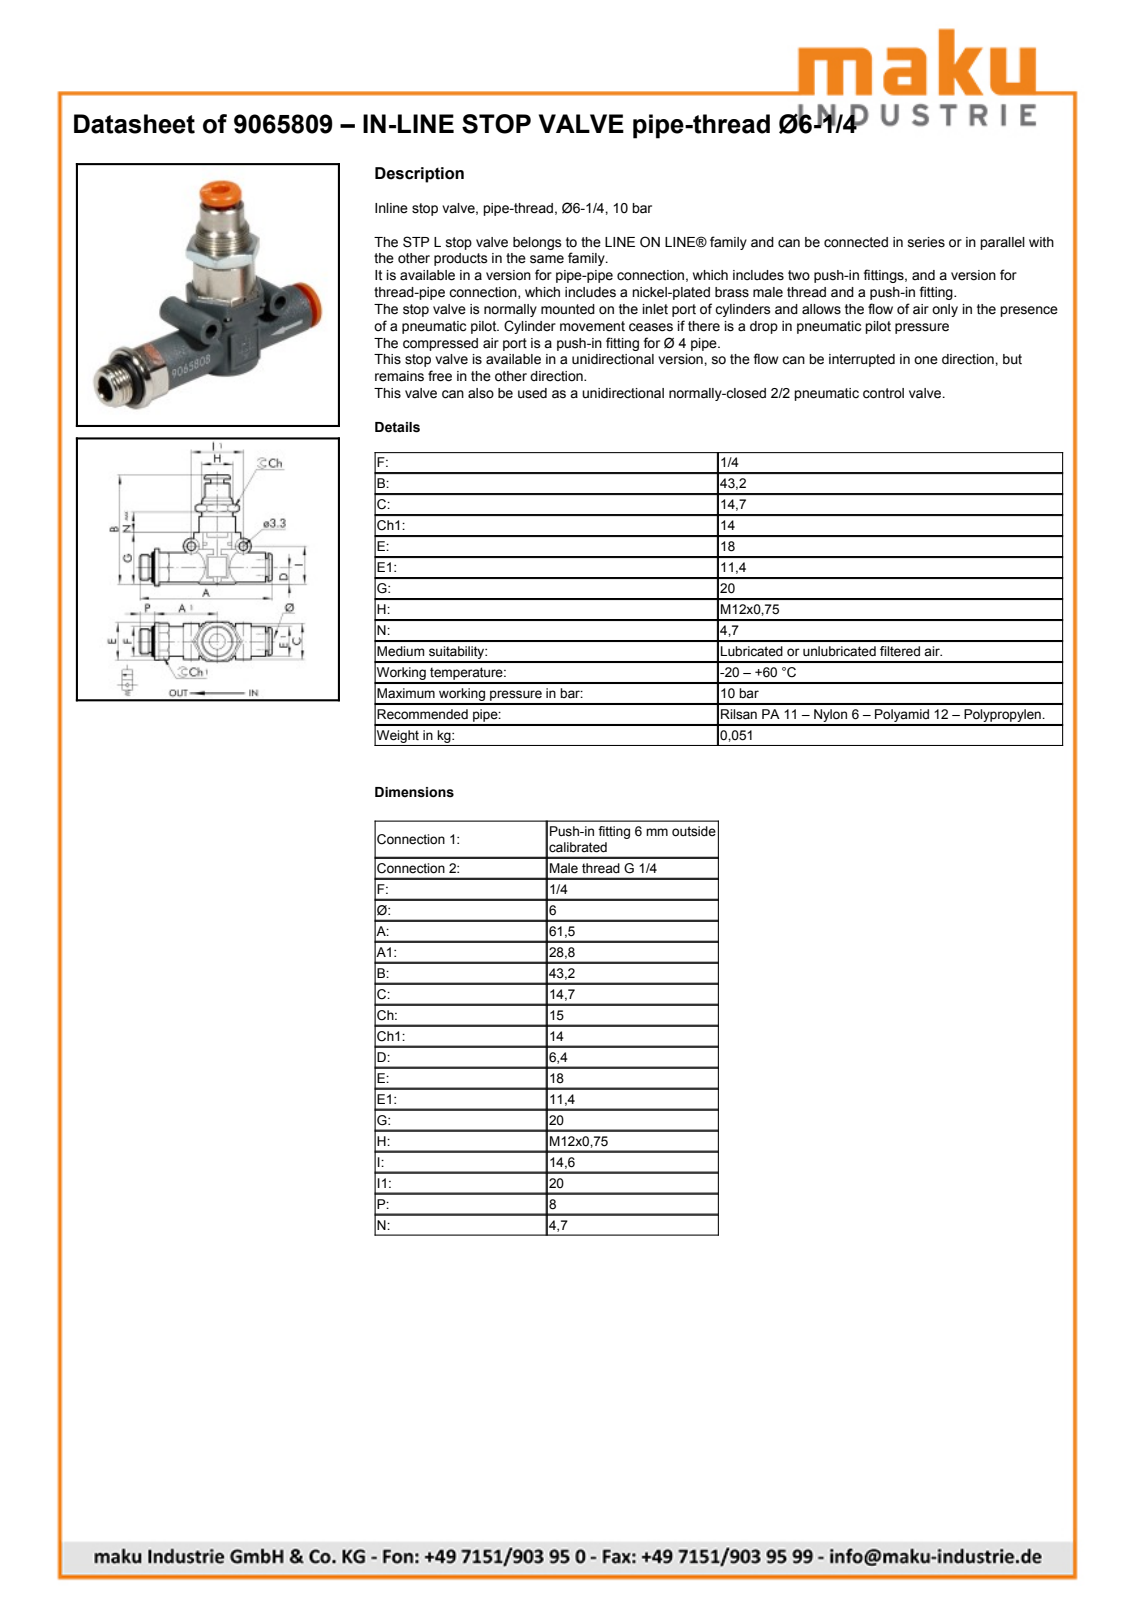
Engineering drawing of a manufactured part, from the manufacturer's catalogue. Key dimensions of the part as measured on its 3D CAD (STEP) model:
Part name (STEP PRODUCT): 9065809; LINE-ON-LINE D6 PNV_L-body; LINE-ON-LINE D6 VNR-L bushing; LINE-ON-LINE D6-1/4 RML-thread port (+2 more)
STEP written by: PARTsolutions (AUTOMOTIVE_DESIGN)
Units: millimetres
Bodies: 5 solids, 175 faces (102 planar, 57 cylindrical, 16 other)
Overall size (bounding box): 61.5 × 45.8 × 18
Volume: 8 362 mm³ · Surface area: 8 447 mm²
Round holes (diameter × count): ⌀3.3 ×2, ⌀4 ×1, ⌀4.5 ×1, ⌀5.53 ×1, ⌀6 ×1, ⌀6.2 ×1, ⌀8 ×1, ⌀9 ×1, ⌀9.6 ×1, ⌀10.3 ×1, ⌀11.6 ×1
Round bosses / shafts (diameter × count): ⌀6 ×2, ⌀18 ×1, ⌀14.8 ×1, ⌀13.8 ×1, ⌀13.16 ×1, ⌀12 ×1, ⌀11.4 ×1, ⌀11.1 ×1
Partial cylindrical surfaces — rounded edges, fillets, slot ends (radius × count): R7.95 ×2, R3.75 ×1, R7.9 ×1, R9.15 ×1
Main face-to-face distances: 14, 18.4, 2, 1.4, 0.4, 14.1, 7.8, 17, 14.2, 14.6
Hole centre spacings: 12.74, 20
